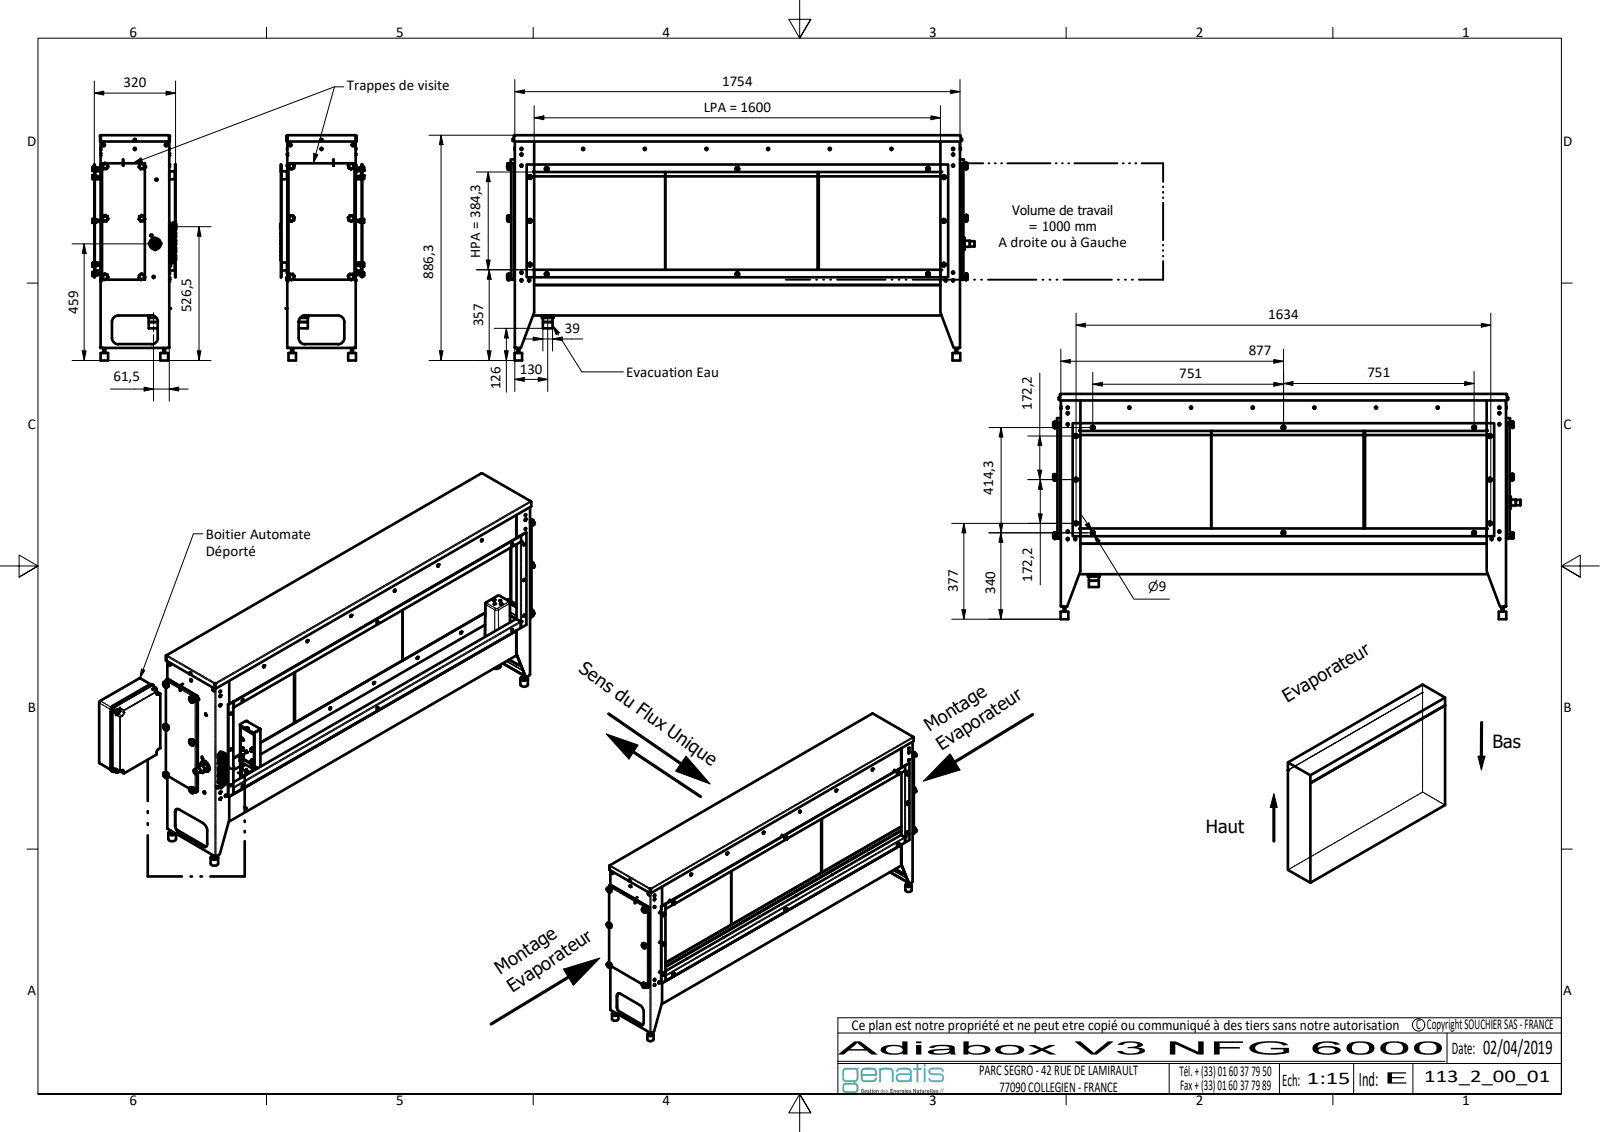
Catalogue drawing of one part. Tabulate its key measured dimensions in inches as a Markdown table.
| quantity | value |
| --- | --- |
| part name | 113_2_00_01_-_Adiabox_V3; 113_2_00_06_-_Glissiere basse assemblee; 113_3_00_11_-_Cote gauche glissiere; 113_3_00_15_-_Tole de fond pliee (+8 more) |
| STEP written by | Autodesk Inventor 2022 (AUTOMOTIVE_DESIGN) |
| units | inches |
| bodies | 328 solids, 9039 faces (4556 planar, 2583 cylindrical, 1900 other) |
| overall size | 72.461 × 34.894 × 12.736 |
| volume | 8 173 in³ |
| surface area | 24 686 in² |
| round holes (diameter × count) | 0.165 × 67, 0.118 × 59, 0.236 × 47, 0.163 × 42, 0.354 × 15, 0.276 × 13, 0.205 × 12, 0.63 × 9, 0.039 × 8, 0.062 × 8, 0.083 × 8, 0.087 × 8 |
| round bosses / shafts (diameter × count) | 0.311 × 59, 0.157 × 59, 0.433 × 46, 0.197 × 40, 0.276 × 37, 0.335 × 22, 0.079 × 10, 0.906 × 8 |
| partial cylindrical surfaces (radius × count) | 0.118 × 176, 0.059 × 91, 0.315 × 84, 0.004 × 36, 0.012 × 36, 0.039 × 30, 0.02 × 26, 0.079 × 23 |
| main face-to-face distances | 0.059, 10.433, 3.937, 0.02, 0.079, 2.441, 27.866, 25.425, 10.492, 0.118 |
| hole center spacings | 9.561, 19.122, 28.684, 38.245, 22.001, 27.537, 9.608, 0.945 |
